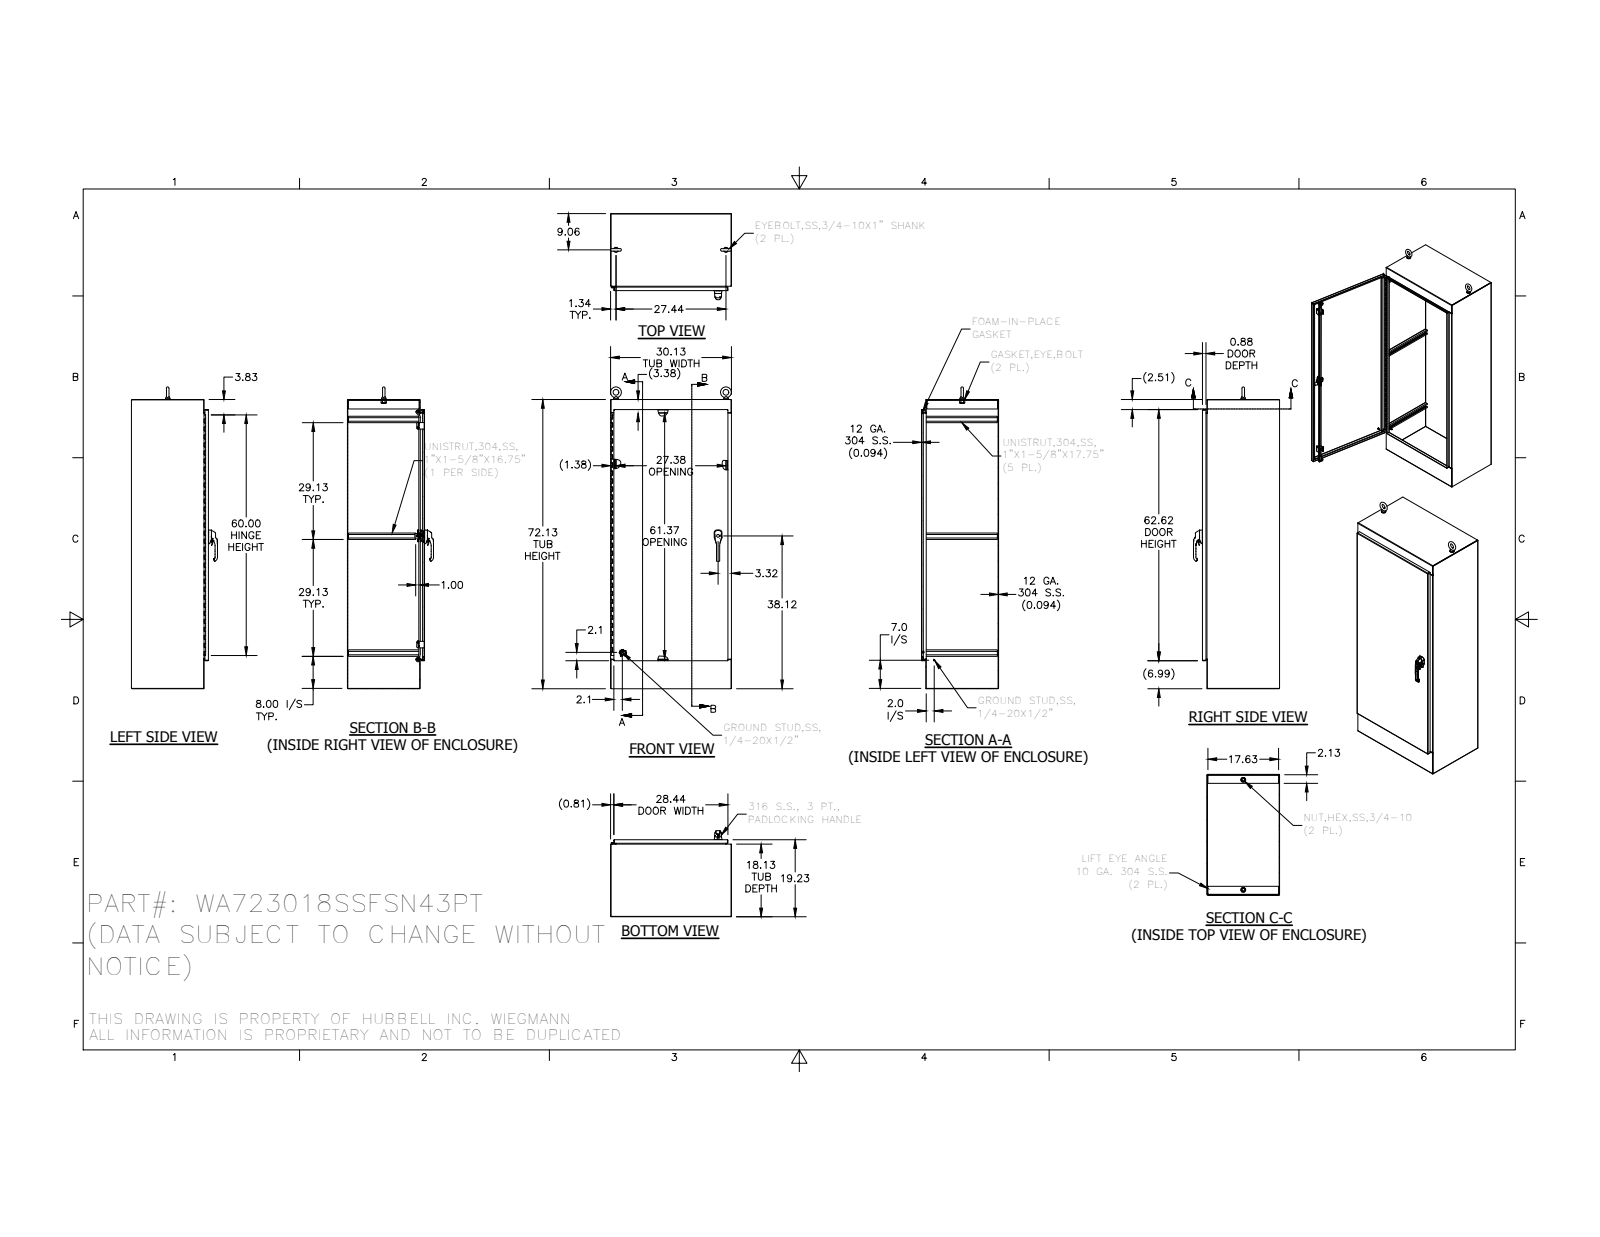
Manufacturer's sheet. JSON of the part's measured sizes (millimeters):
{"part_name": "WA18SSFSN43PT-EBA; 2100-11; HFW31712; 328131L-60 (+8 more)", "step_written_by": "SolidWorks 2014 (AUTOMOTIVE_DESIGN)", "units": "millimeters", "bodies": {"solids": 64, "faces": 3471, "planar": 1220, "cylindrical": 1311, "other": 940}, "overall_size": [1911.3, 765.2, 545.5], "volume_mm3": 15220000, "surface_area_mm2": 12370000, "round_holes": [[6.7, 8], [9.5, 8], [4.7, 4], [5.4, 3], [6.4, 3], [7.1, 3], [6.1, 2], [6.4, 2], [8, 2], [10.2, 2], [10.2, 2], [10.5, 2]], "round_bosses_or_shafts": [[25.4, 3], [6, 3], [31.8, 2], [28.4, 2], [19.1, 2], [14.3, 2], [13.5, 2], [13.5, 2]], "partial_cylinders_radius": [[0.5, 172], [0.3, 107], [3.2, 26], [0.5, 21], [0.8, 19], [1.3, 19], [3.2, 15], [2, 14]], "face_to_face_distances": [2.4, 486, 762.8, 483.6, 488.4, 760.4, 765.2, 1829.6, 458, 28], "hole_center_spacings": [169.3, 508, 9.7, 19.3, 70.2, 338.7, 677.3, 804.3]}
